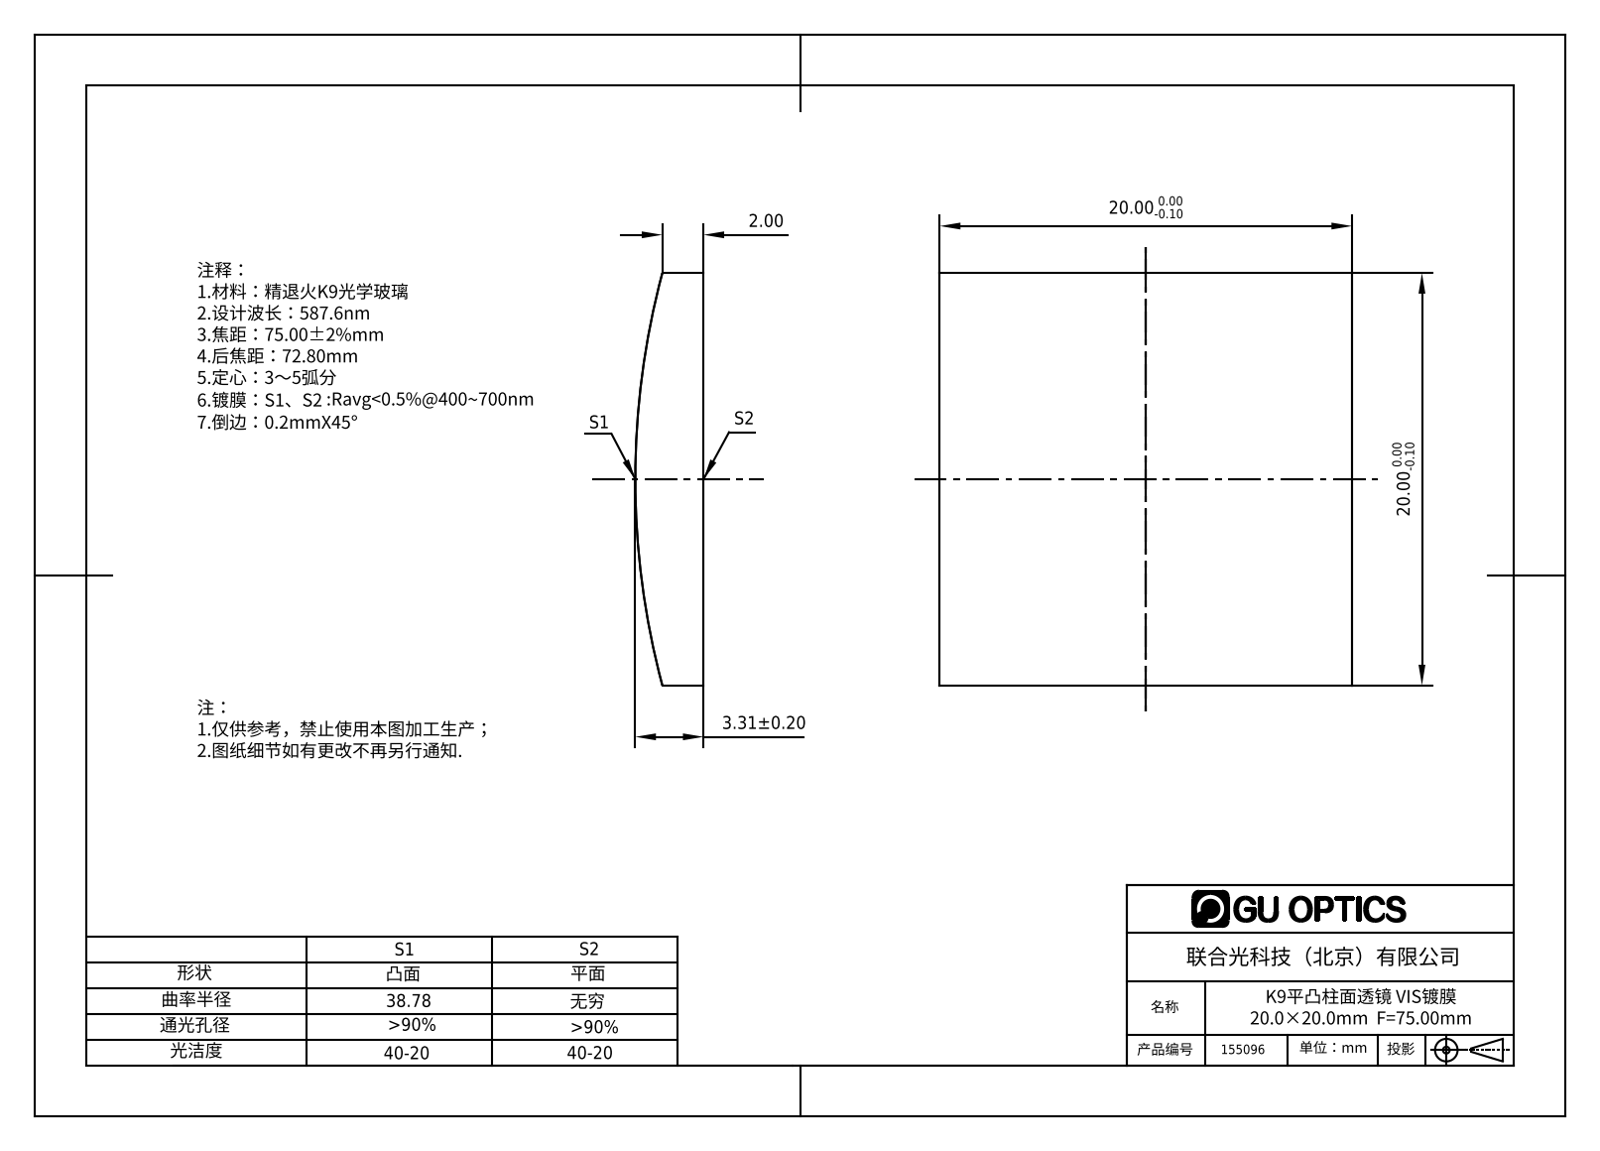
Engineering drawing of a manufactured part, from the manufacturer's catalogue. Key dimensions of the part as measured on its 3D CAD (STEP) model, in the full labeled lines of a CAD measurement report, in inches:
Part name (STEP PRODUCT): 155030
STEP written by: SolidWorks 2016 (AUTOMOTIVE_DESIGN)
Units: inches
Bodies: 1 solid, 6 faces (5 planar, 1 cylindrical, 0 other)
Overall size (bounding box): 0.787 × 0.787 × 0.13
Volume: 0.07 in³ · Surface area: 1.55 in²
Partial cylindrical surfaces — rounded edges, fillets, slot ends (radius × count): R1.527 ×1
Main face-to-face distances: 0.787
